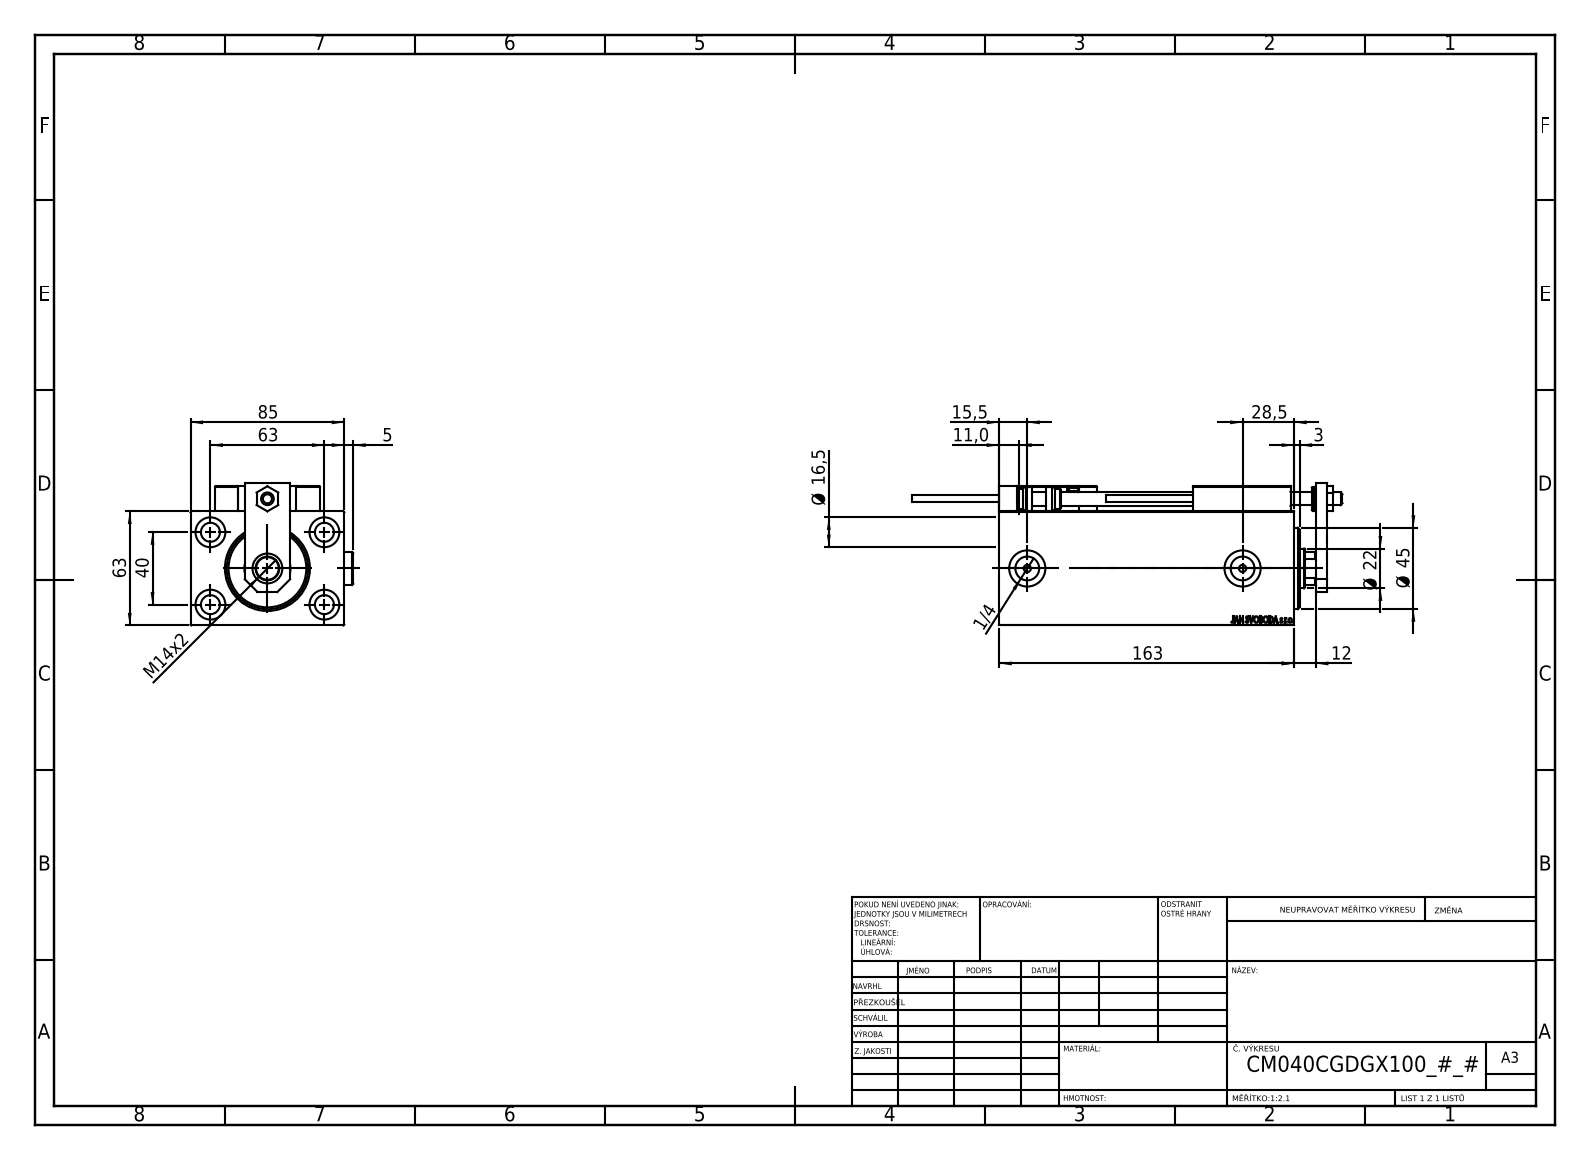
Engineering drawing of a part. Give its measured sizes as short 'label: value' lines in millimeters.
name: MAGNET; NUT_D12; KONCOVKA; SWITCH_X_FRONT_BACK (+7 more)
written by: SolidWorks 2019 (CONFIG_CONTROL_DESIGN)
unit: mm
bodies: 25 solids, 1336 faces (594 planar, 204 cylindrical, 538 other)
size: 237.7 × 89.9 × 78.5
volume: 769 478 mm³; area: 153 297 mm²
holes: 6× ⌀4, 5× ⌀8, 5× ⌀16.5, 4× ⌀3.2, 4× ⌀10.5, 2× ⌀5, 2× ⌀13.16, 2× ⌀20, 1× ⌀7, 1× ⌀12.5, 1× ⌀22, 1× ⌀25.5
bosses: 2× ⌀18, 2× ⌀5, 2× ⌀3.8, 1× ⌀13, 1× ⌀11
rounds: 30× R0.3, 2× R3, 1× R10.5
face distances: 63, 85, 12, 151, 163, 14, 77, 15, 18, 30
hole spacings: 37.31, 11.37, 20, 29.59, 29.69, 36.06, 36.53, 40
